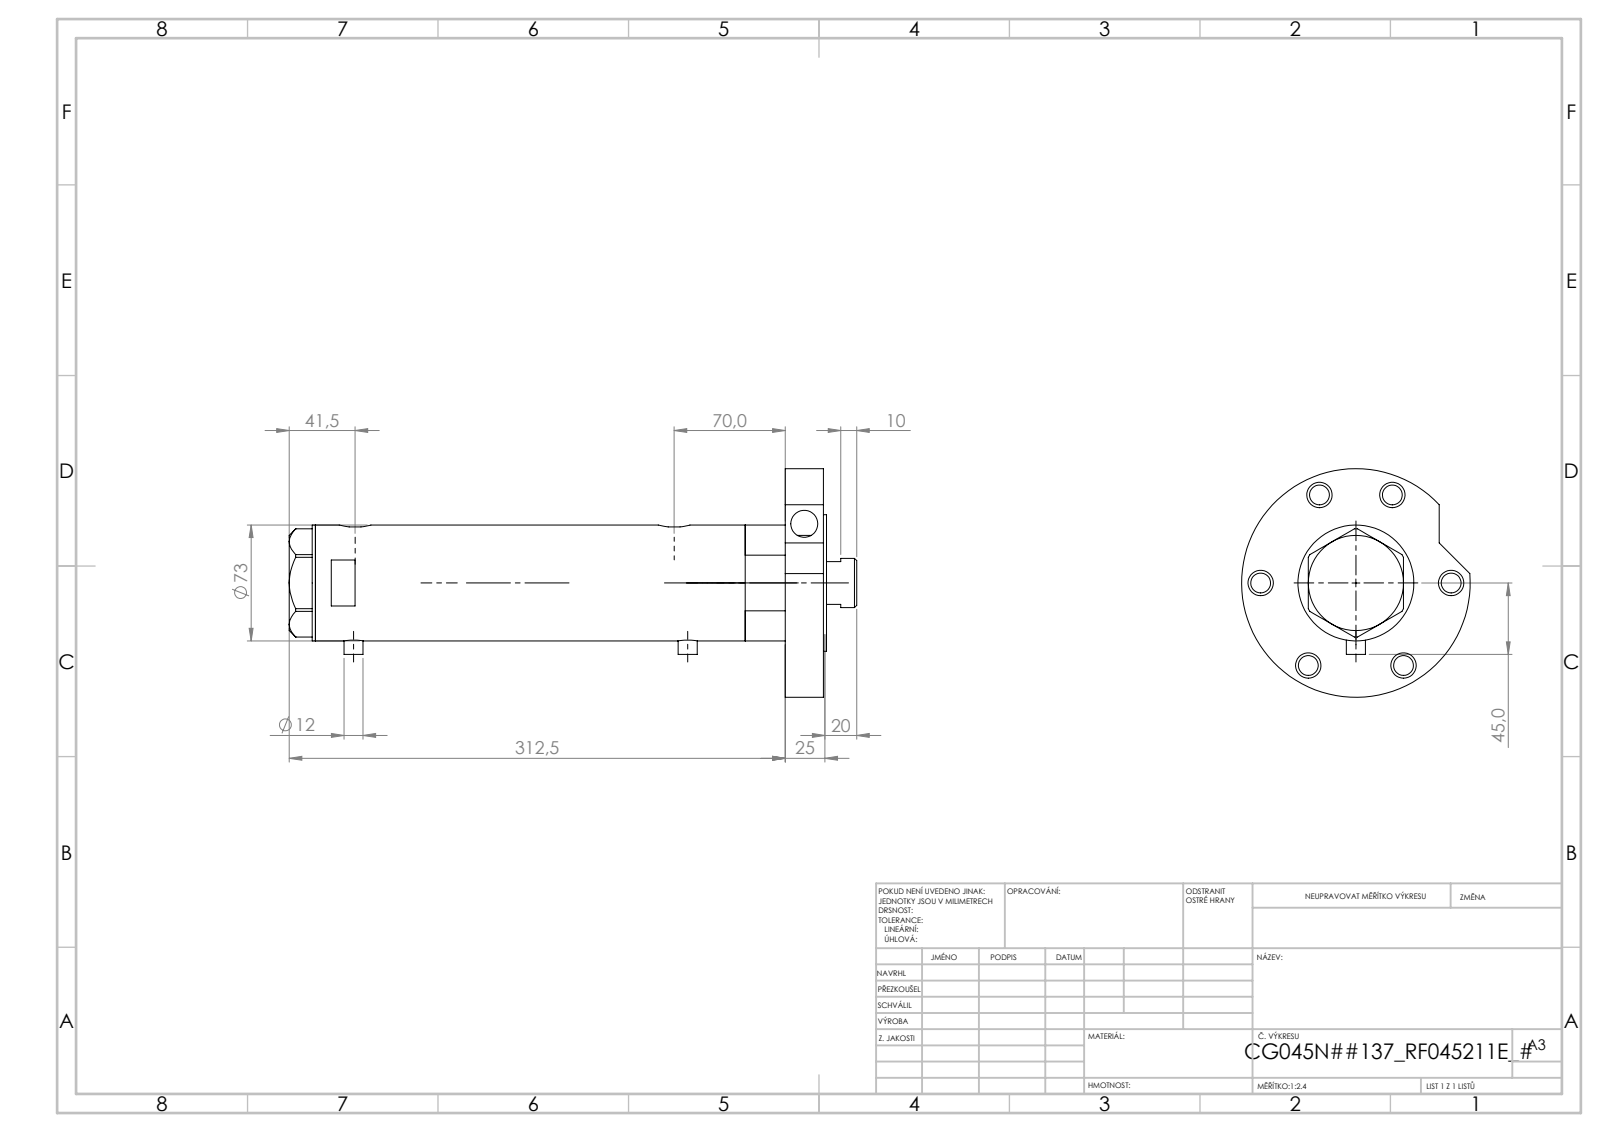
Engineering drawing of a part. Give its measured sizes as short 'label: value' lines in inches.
name: V270CG_BACK; V270CG_VC; V270CG_FRONT; V270CG_RF211E (+1 more)
written by: SolidWorks 2019 (CONFIG_CONTROL_DESIGN)
unit: in
bodies: 5 solids, 176 faces (74 planar, 82 cylindrical, 20 other)
size: 7.26 × 5.669 × 5.669
volume: 33.54 in³; area: 208.7 in²
holes: 8× ⌀0.492, 6× ⌀0.63, 2× ⌀0.197, 2× ⌀0.38, 2× ⌀0.591, 1× ⌀0.256, 1× ⌀0.669, 1× ⌀0.787, 1× ⌀0.846, 1× ⌀1.772, 1× ⌀2.362
bosses: 2× ⌀0.472, 1× ⌀5.669, 1× ⌀3.386, 1× ⌀2.047, 1× ⌀1.732, 1× ⌀1.575, 1× ⌀1.496, 1× ⌀1.299
face distances: 0.945, 0.079, 1.024, 4.787, 5.732, 5.811, 6.748, 0.937, 5.724, 6.669
hole spacings: 2.362, 2.625, 3.928, 4.091, 4.237, 4.714, 0.114, 0.177
